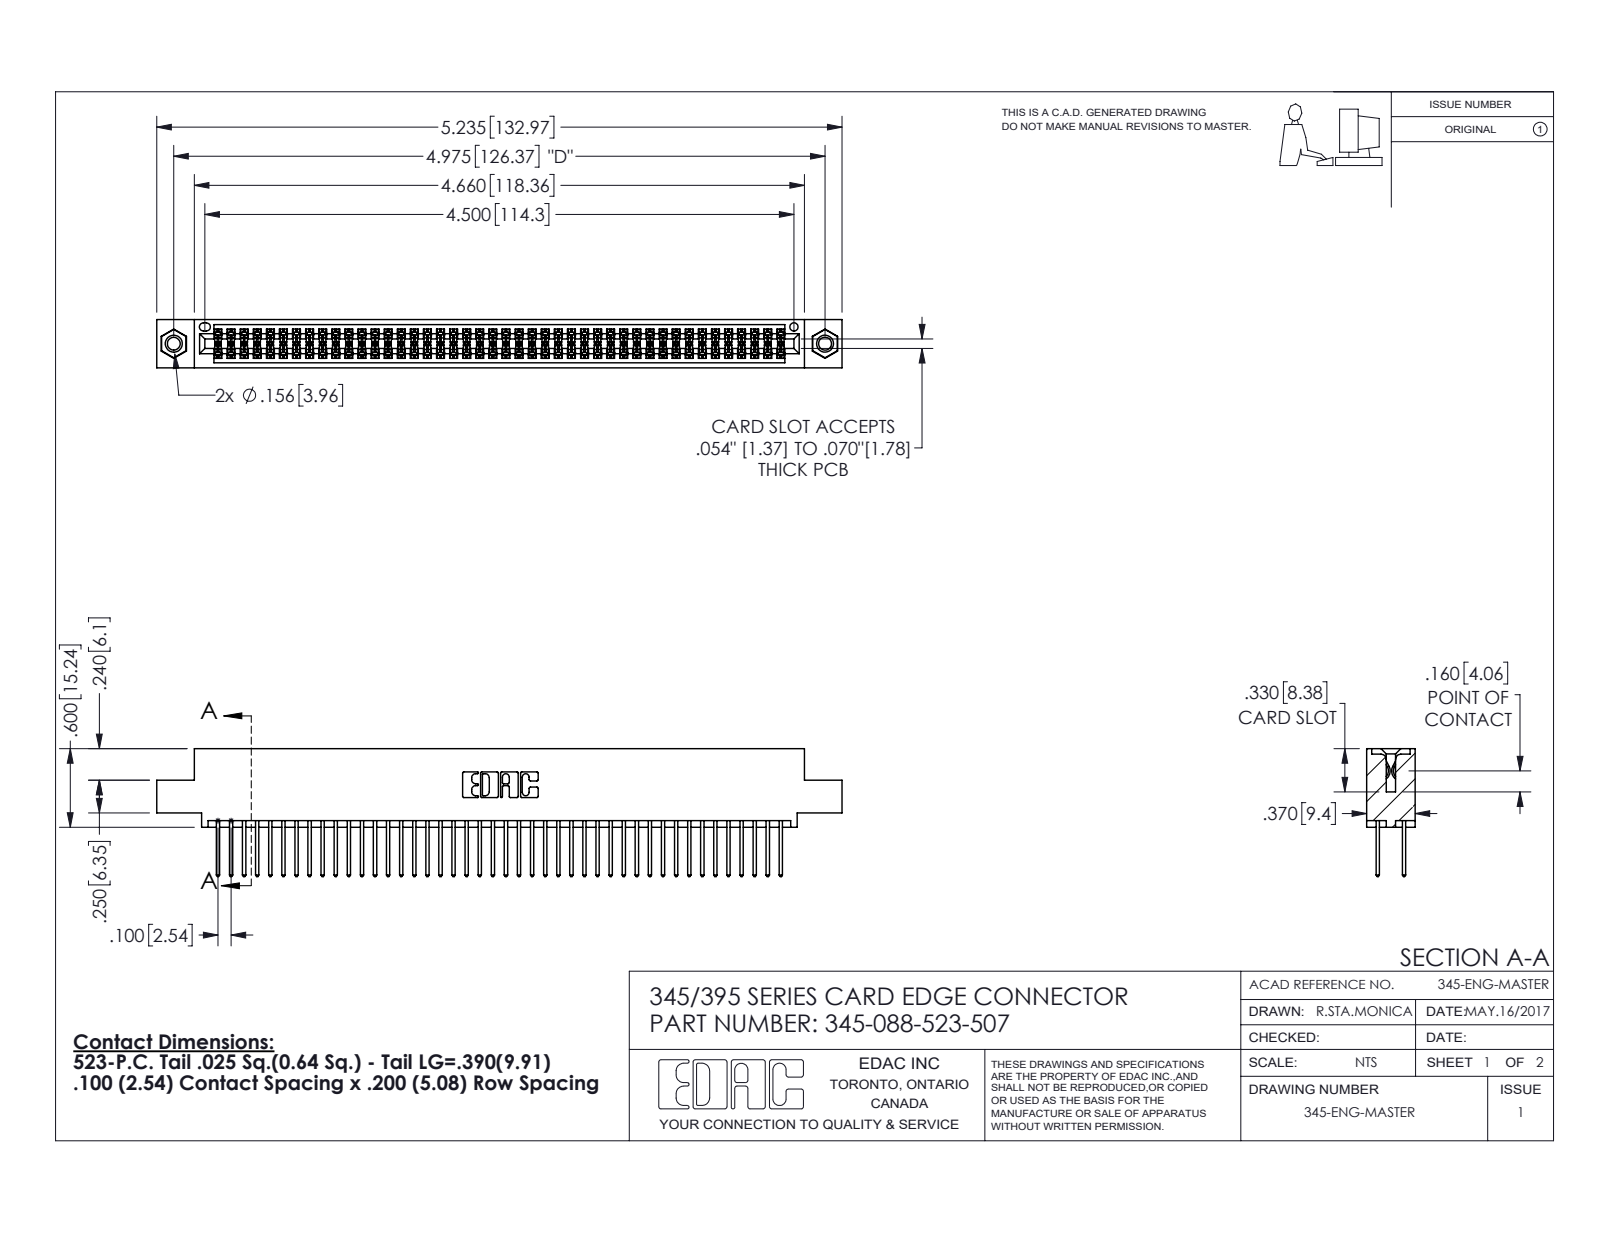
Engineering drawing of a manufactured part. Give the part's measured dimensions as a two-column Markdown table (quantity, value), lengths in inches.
| quantity | value |
| --- | --- |
| part name | 345-292-001_345-293-123; 345 Part_0.110 Offset - 0.156 Dia-TI; 345-088-523-507; 345-250-001_345-250-005-103 |
| STEP written by | SolidWorks 2016 (CONFIG_CONTROL_DESIGN) |
| units | inches |
| bodies | 91 solids, 4590 faces (3020 planar, 1554 cylindrical, 16 other) |
| overall size | 5.235 × 0.977 × 0.37 |
| volume | 0.795 in³ |
| surface area | 31.35 in² |
| round holes (diameter × count) | 0.098 × 2, 0.125 × 2, 0.156 × 2, 0.064 × 1 |
| round bosses / shafts (diameter × count) | 0.155 × 2 |
| partial cylindrical surfaces (radius × count) | 0.006 × 132, 0.01 × 88, 0.01 × 22, 0.007 × 6, 0.031 × 6, 0.026 × 3, 0.014 × 2, 0.019 × 2 |
| main face-to-face distances | 0.072, 0.298, 0.2, 0.098, 0.272, 0.025, 0.37, 0.225, 0.175, 0.149 |
| hole center spacings | 0.27, 4.739, 4.975 |
